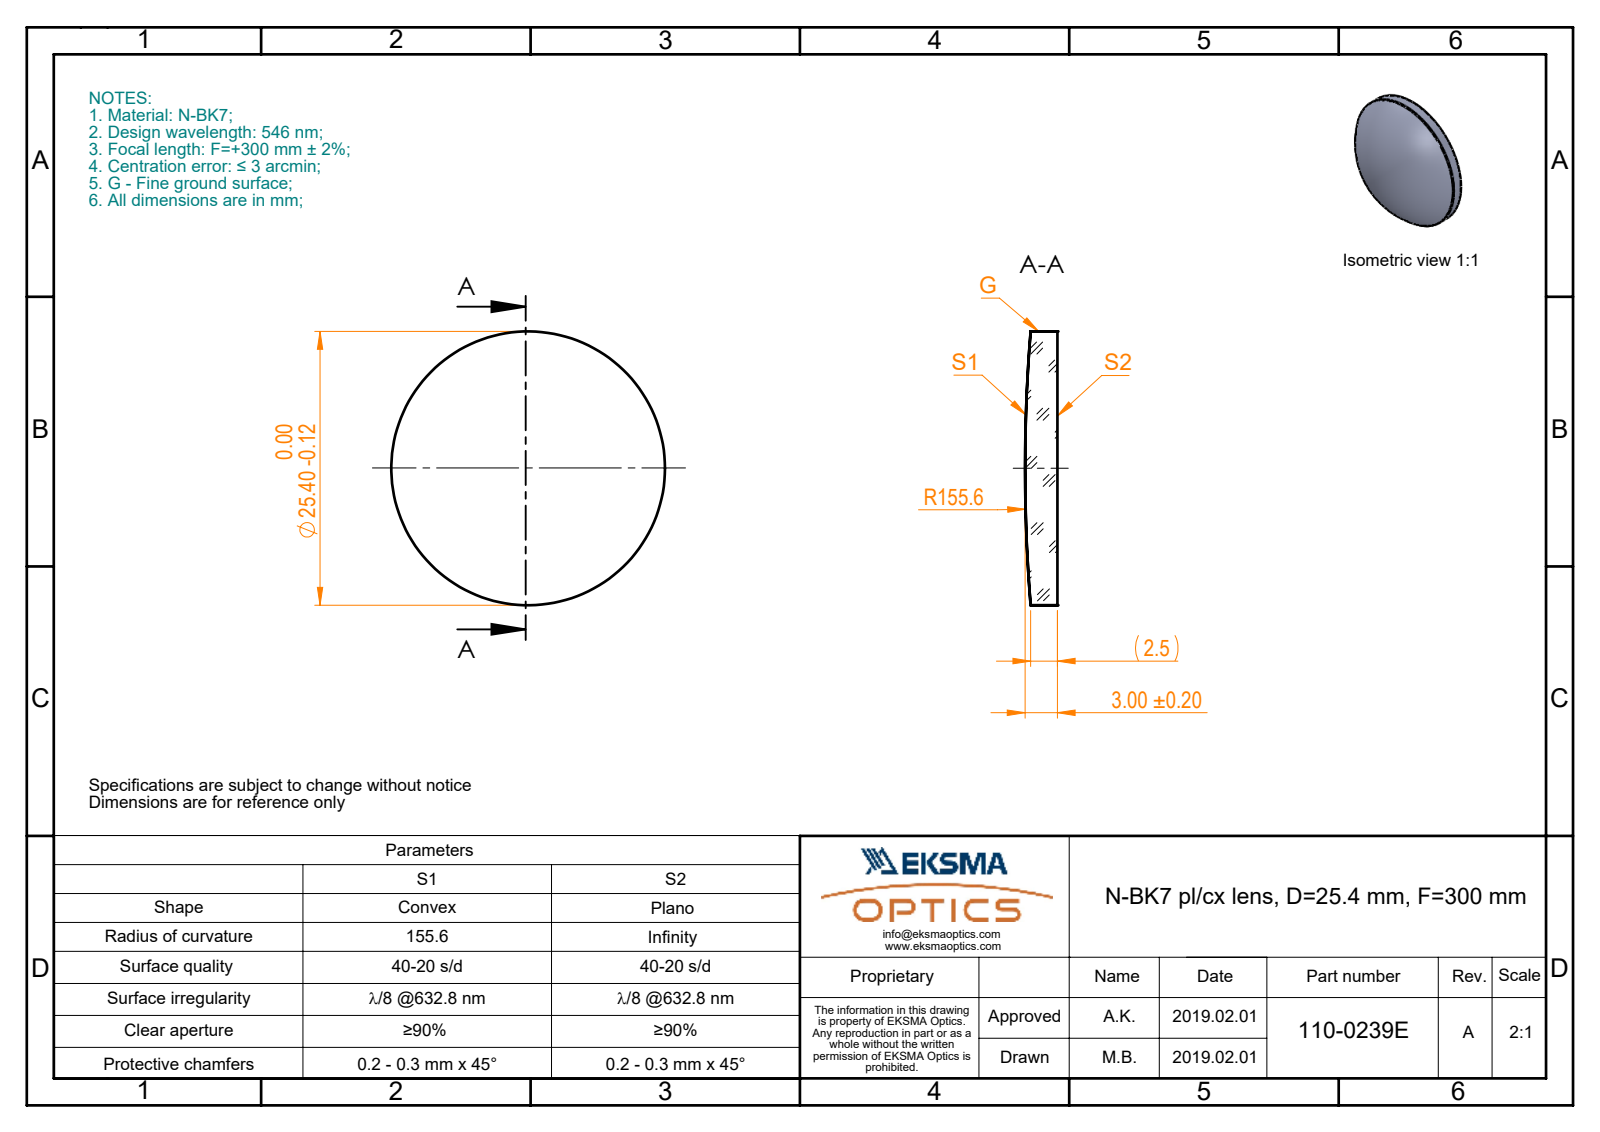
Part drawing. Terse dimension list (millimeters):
name: 110-0239E BK7 pl-cx 25.4 F300
written by: SolidWorks 2017 (CONFIG_CONTROL_DESIGN)
unit: mm
bodies: 1 solid, 5 faces (1 planar, 2 cylindrical, 2 other)
size: 25.4 × 25.4 × 3
volume: 1 389 mm³; area: 1 212 mm²
bosses: 1× ⌀25.4
